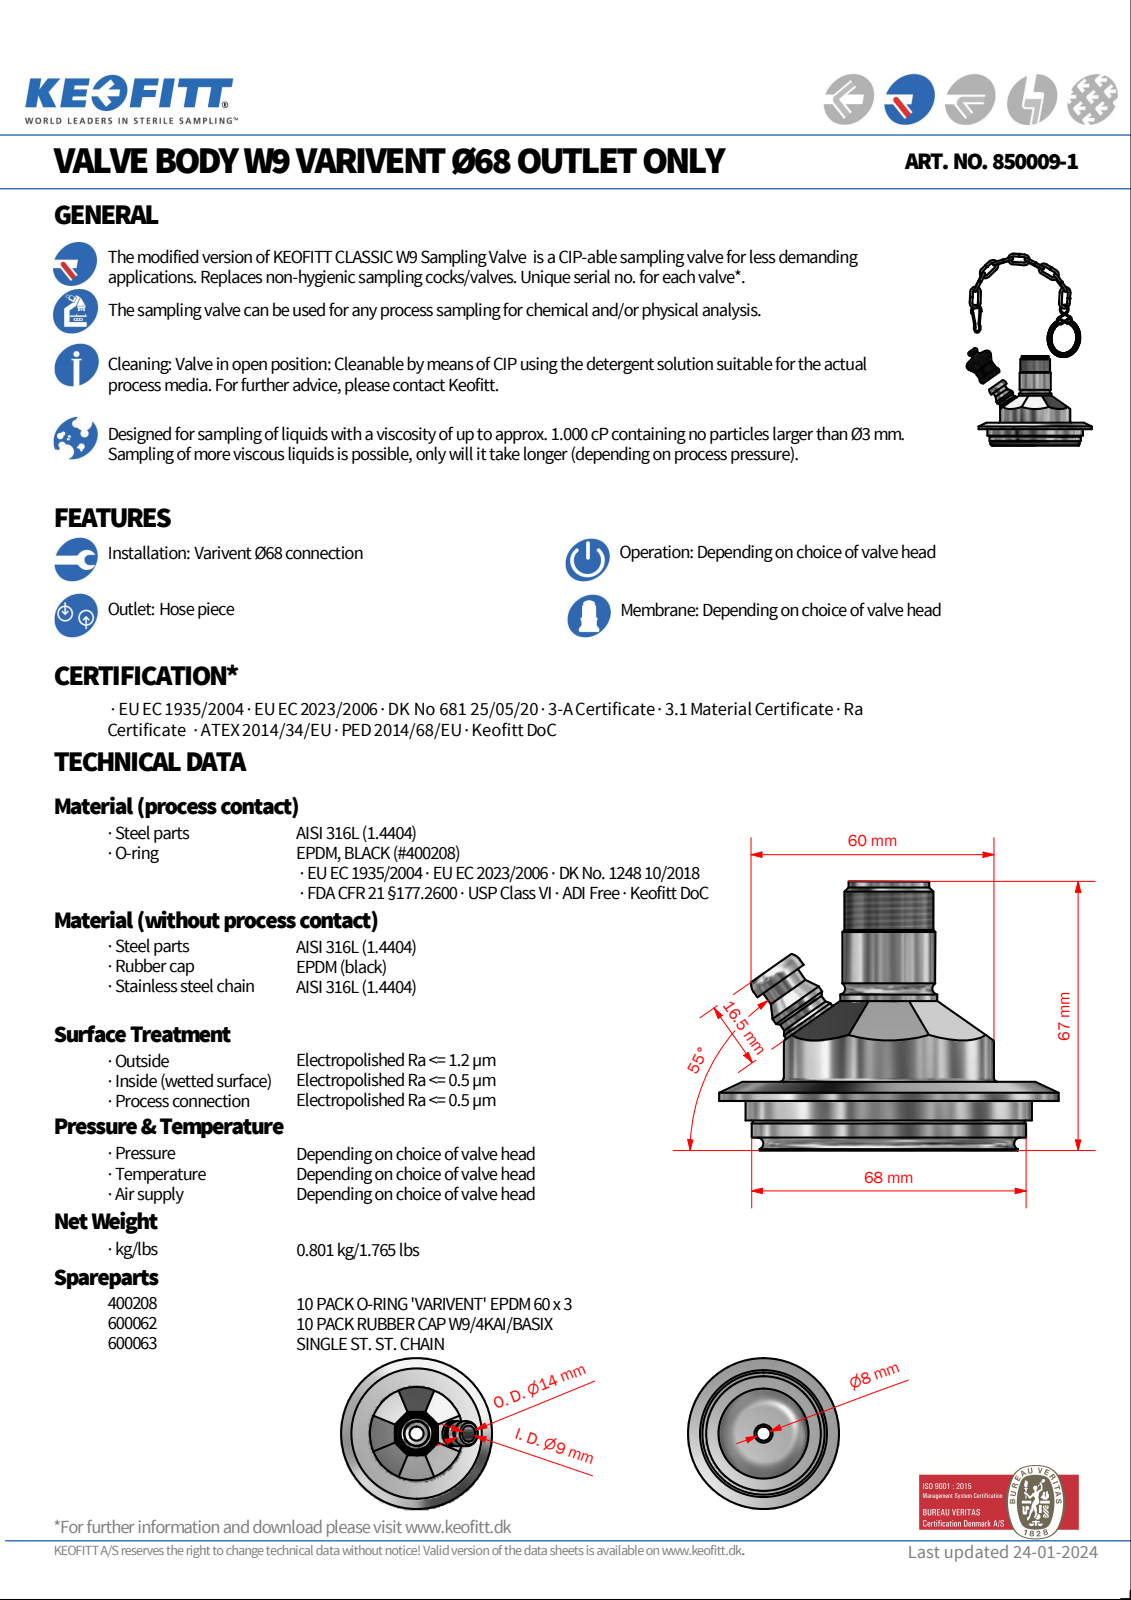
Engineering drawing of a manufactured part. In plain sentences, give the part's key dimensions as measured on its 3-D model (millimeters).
The part is named "850009-1". Its 3-D file was written by "Autodesk Inventor 2020 (AUTOMOTIVE_DESIGN)". It is 1 solid with 68 faces: 24 planar, 23 cylindrical and 21 other. Overall it measures 84 by 84 by 66.62 millimeters. Its volume is 107 370 cubic millimeters and its surface area 25 965 square millimeters. Round holes: 1 of diameter 9, 1 of diameter 18.1, 1 of diameter 21, 1 of diameter 22. Round bosses or shafts: 3 of diameter 14, 1 of diameter 84, 1 of diameter 70.85, 1 of diameter 67.9, 1 of diameter 63.9, 1 of diameter 52, 1 of diameter 24, 1 of diameter 23. The main face-to-face distances are 4.75, 12.25, 17, 2, 10.25, 15, 7.5, 5.5, 9.5, 3.25.
